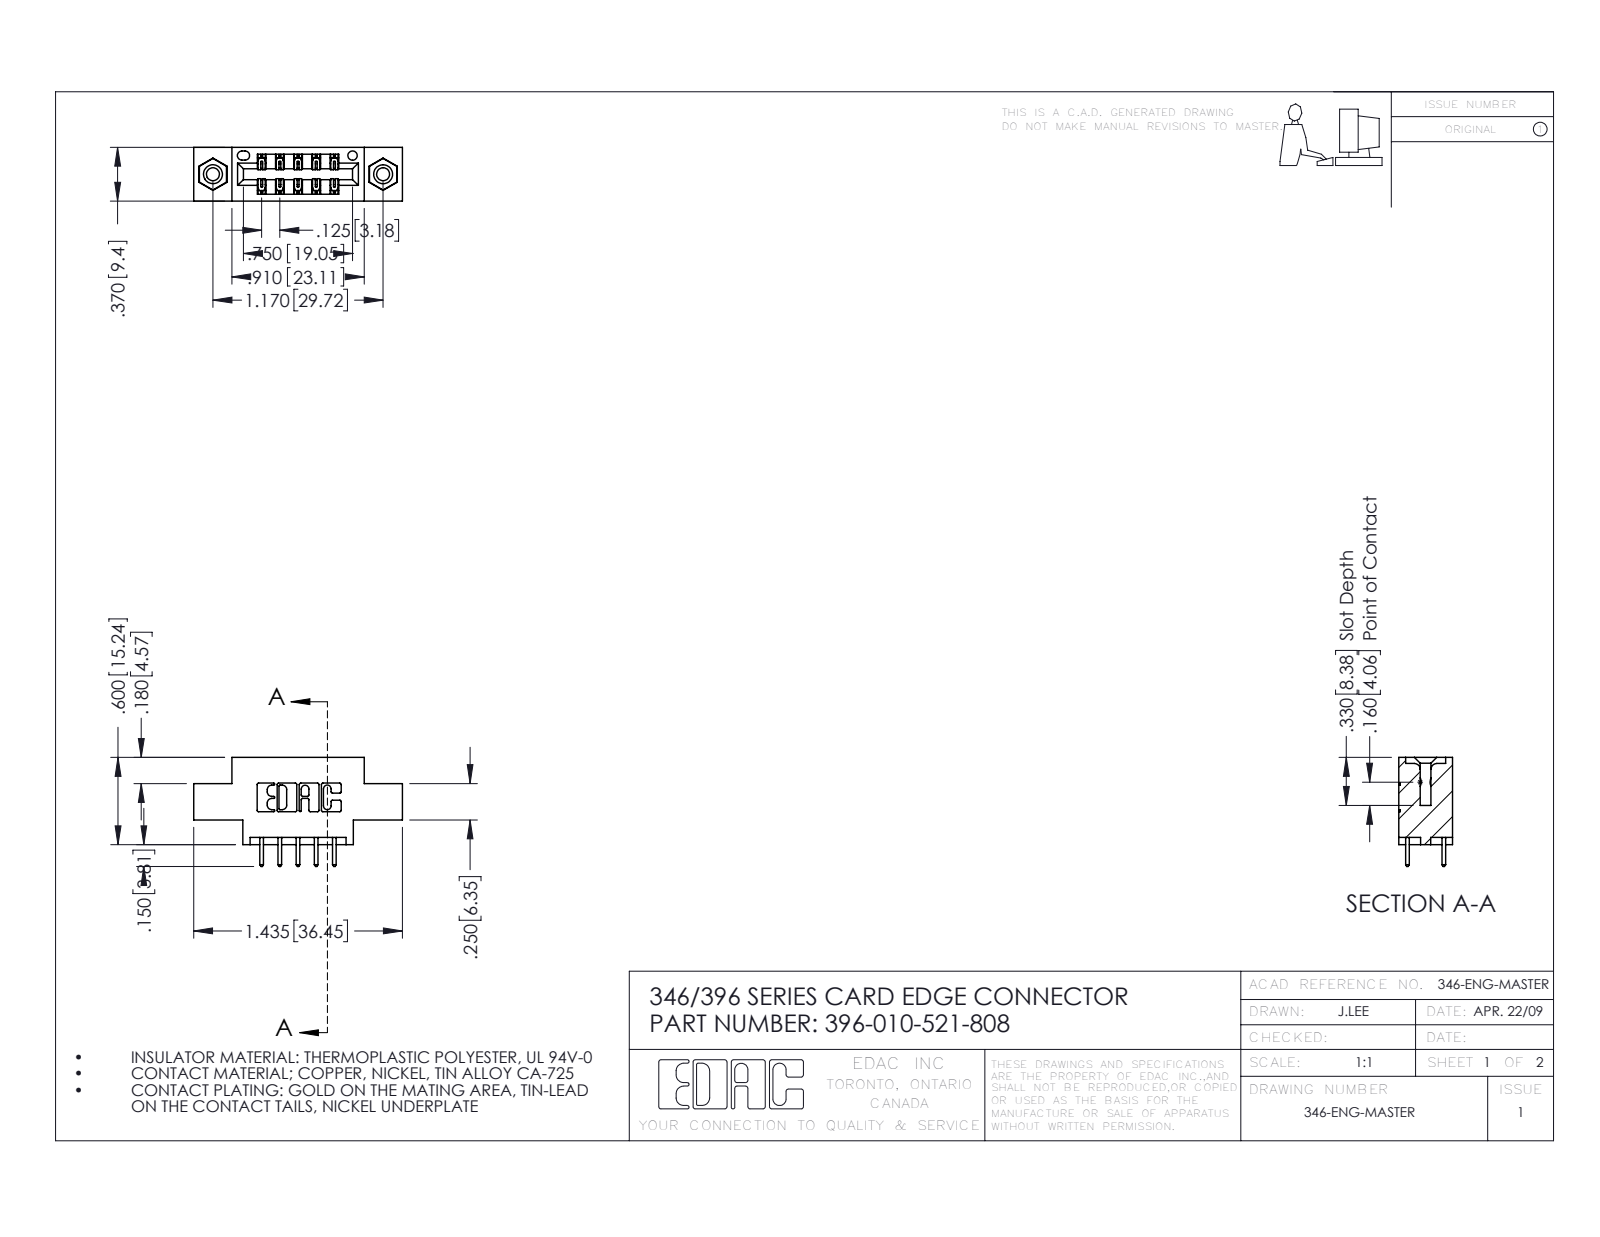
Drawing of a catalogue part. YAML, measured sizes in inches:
part_name: "396-010-521-808; 346 Part_0.170 Offset - 0.156 Dia-TI; 345-250-001_345-250-003-102; 345-292-001_345-293-121"
step_written_by: "SolidWorks 2016 (CONFIG_CONTROL_DESIGN)"
units: inches
bodies: {solids: 13, faces: 706, planar: 462, cylindrical: 228, other: 16}
overall_size: [1.435, 0.75, 0.37]
volume: 0.189
surface_area: 5.974
round_holes:
  - {diameter: 0.089, count: 2}
  - {diameter: 0.125, count: 2}
  - {diameter: 0.156, count: 2}
  - {diameter: 0.064, count: 1}
round_bosses_or_shafts:
  - {diameter: 0.155, count: 2}
partial_cylinders:
  - {radius: 0.01, count: 22}
  - {radius: 0.006, count: 15}
  - {radius: 0.01, count: 10}
  - {radius: 0.007, count: 6}
  - {radius: 0.031, count: 6}
  - {radius: 0.026, count: 3}
  - {radius: 0.014, count: 2}
  - {radius: 0.022, count: 2}
face_to_face_distances: [0.25, 0.37, 0.048, 0.322, 0.222, 0.148, 0.072, 0.298, 0.025, 0.1]
hole_center_spacings: [0.246, 0.969, 1.17]
